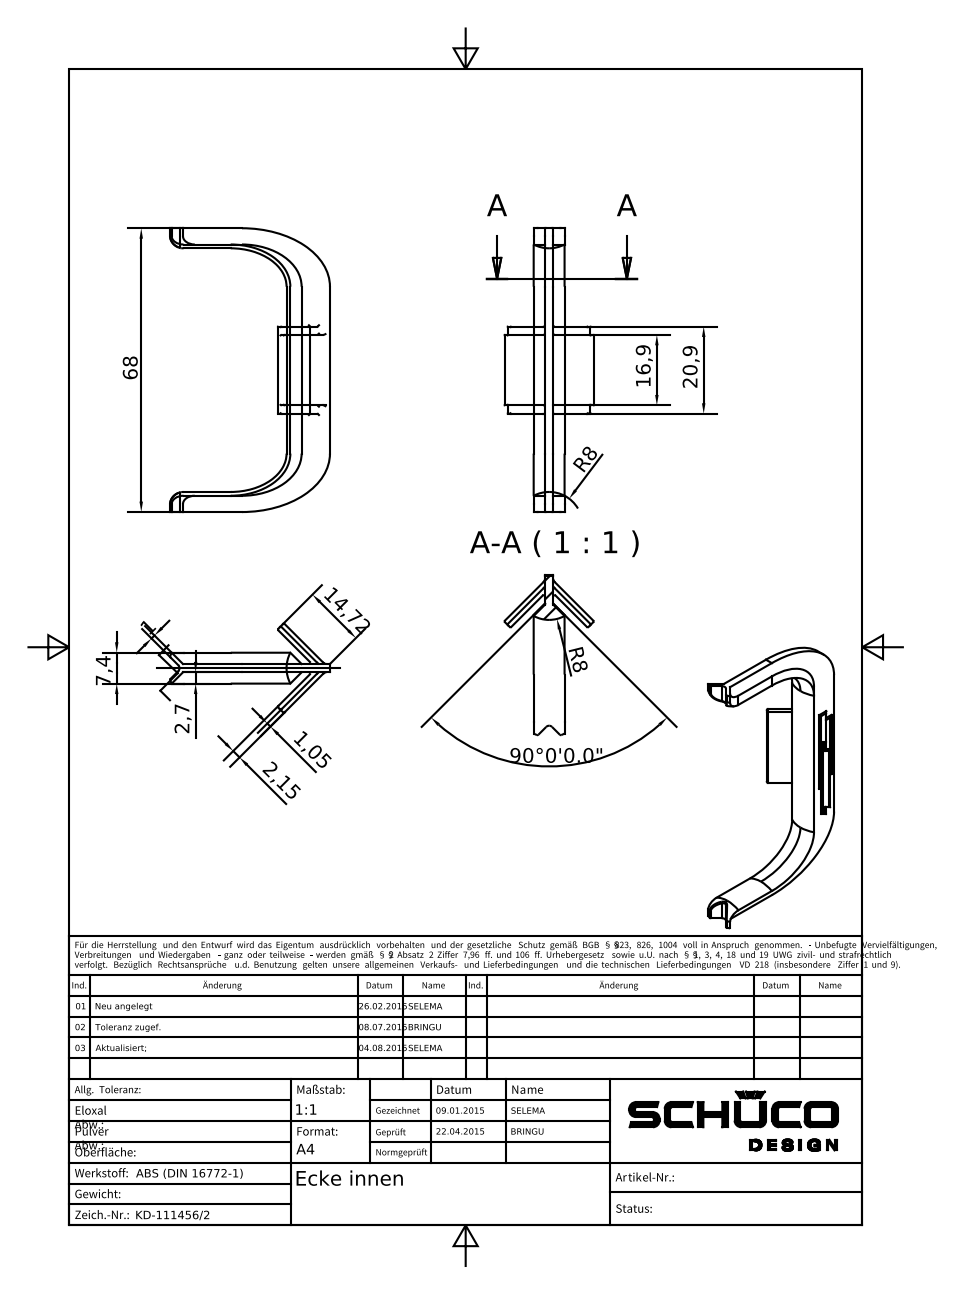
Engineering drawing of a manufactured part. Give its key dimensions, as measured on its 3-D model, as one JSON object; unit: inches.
{"part_name": "KD-111456", "step_written_by": "Autodesk Inventor 2024 (AUTOMOTIVE_DESIGN)", "units": "inches", "bodies": {"solids": 1, "faces": 107, "planar": 37, "cylindrical": 52, "other": 18}, "overall_size": [2.677, 1.187, 1.187], "volume_in3": 0.218, "surface_area_in2": 6.513, "partial_cylinders_radius": [[0.012, 27], [0.079, 4], [0.315, 4], [0.398, 4], [0.039, 3]], "face_to_face_distances": [0.079, 0.085, 0.154, 0.069, 0.112, 0.043, 0.041, 2.524, 2.37, 0.446]}
